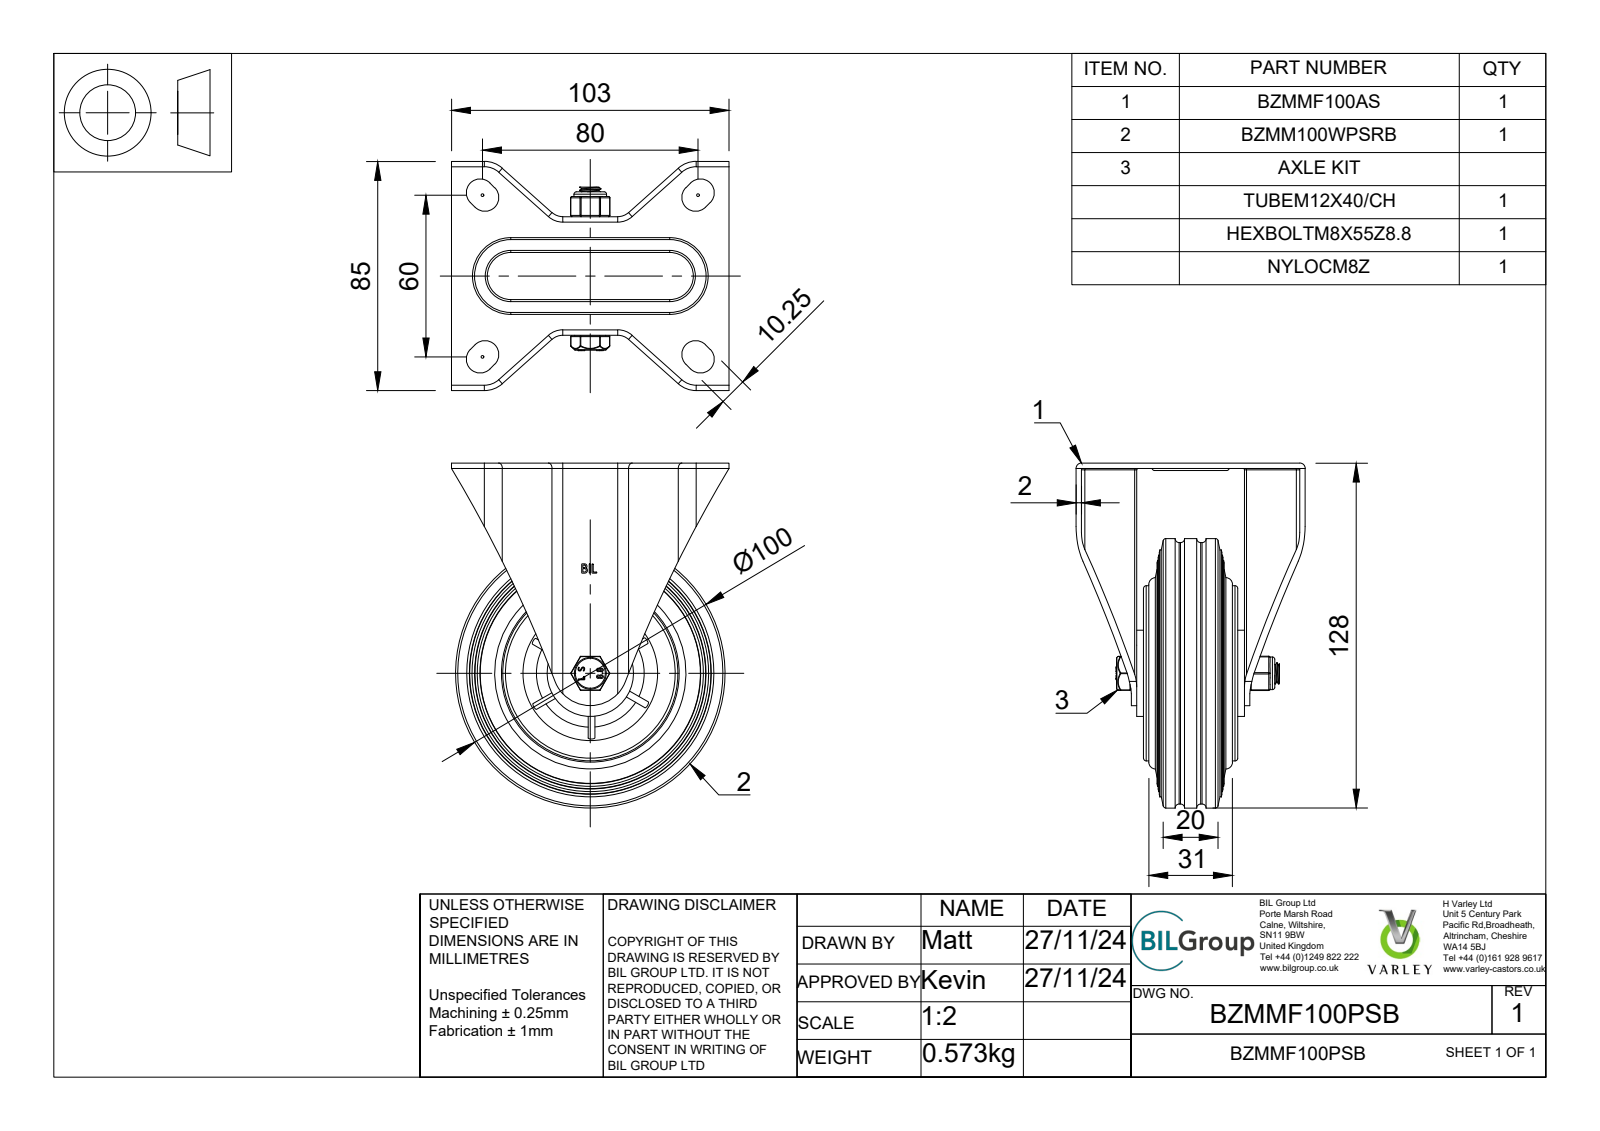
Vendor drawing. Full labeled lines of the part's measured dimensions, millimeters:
Part name (STEP PRODUCT): BZMMF100PSB v3; BZMMF100AS v1; BZMMF100AS; ZINC PLATED, PRESSED STEEL BRACKET (+7 more)
STEP written by: Autodesk Translation Framework v13.20.0.188 (AP242_MANAGED_MODEL_BASED_3D_ENGINEERING_MIM_LF)
Units: millimetres
Bodies: 17 solids, 573 faces (231 planar, 211 cylindrical, 131 other)
Overall size (bounding box): 128 × 103 × 85
Volume: 238 523 mm³ · Surface area: 102 320 mm²
Round holes (diameter × count): ⌀0.66 ×2, ⌀8 ×1, ⌀8.25 ×1, ⌀8.4 ×1, ⌀8.6 ×1, ⌀12.5 ×1, ⌀15 ×1, ⌀15.5 ×1, ⌀21 ×1, ⌀27 ×1
Round bosses / shafts (diameter × count): ⌀3.75 ×8, ⌀100 ×1, ⌀97 ×1, ⌀65 ×1, ⌀32 ×1, ⌀19.5 ×1, ⌀12.1 ×1, ⌀11.9 ×1
Partial cylindrical surfaces — rounded edges, fillets, slot ends (radius × count): R0.5 ×26, R0.25 ×12, R1.25 ×12, R0.75 ×8, R2 ×8, R5.12 ×8, R0.33 ×4, R0.64 ×4
Main face-to-face distances: 2, 4.5, 37.5, 35.5, 14.26, 2.5, 42, 6.5, 40, 12.26
Hole centre spacings: 3.22, 2.49
